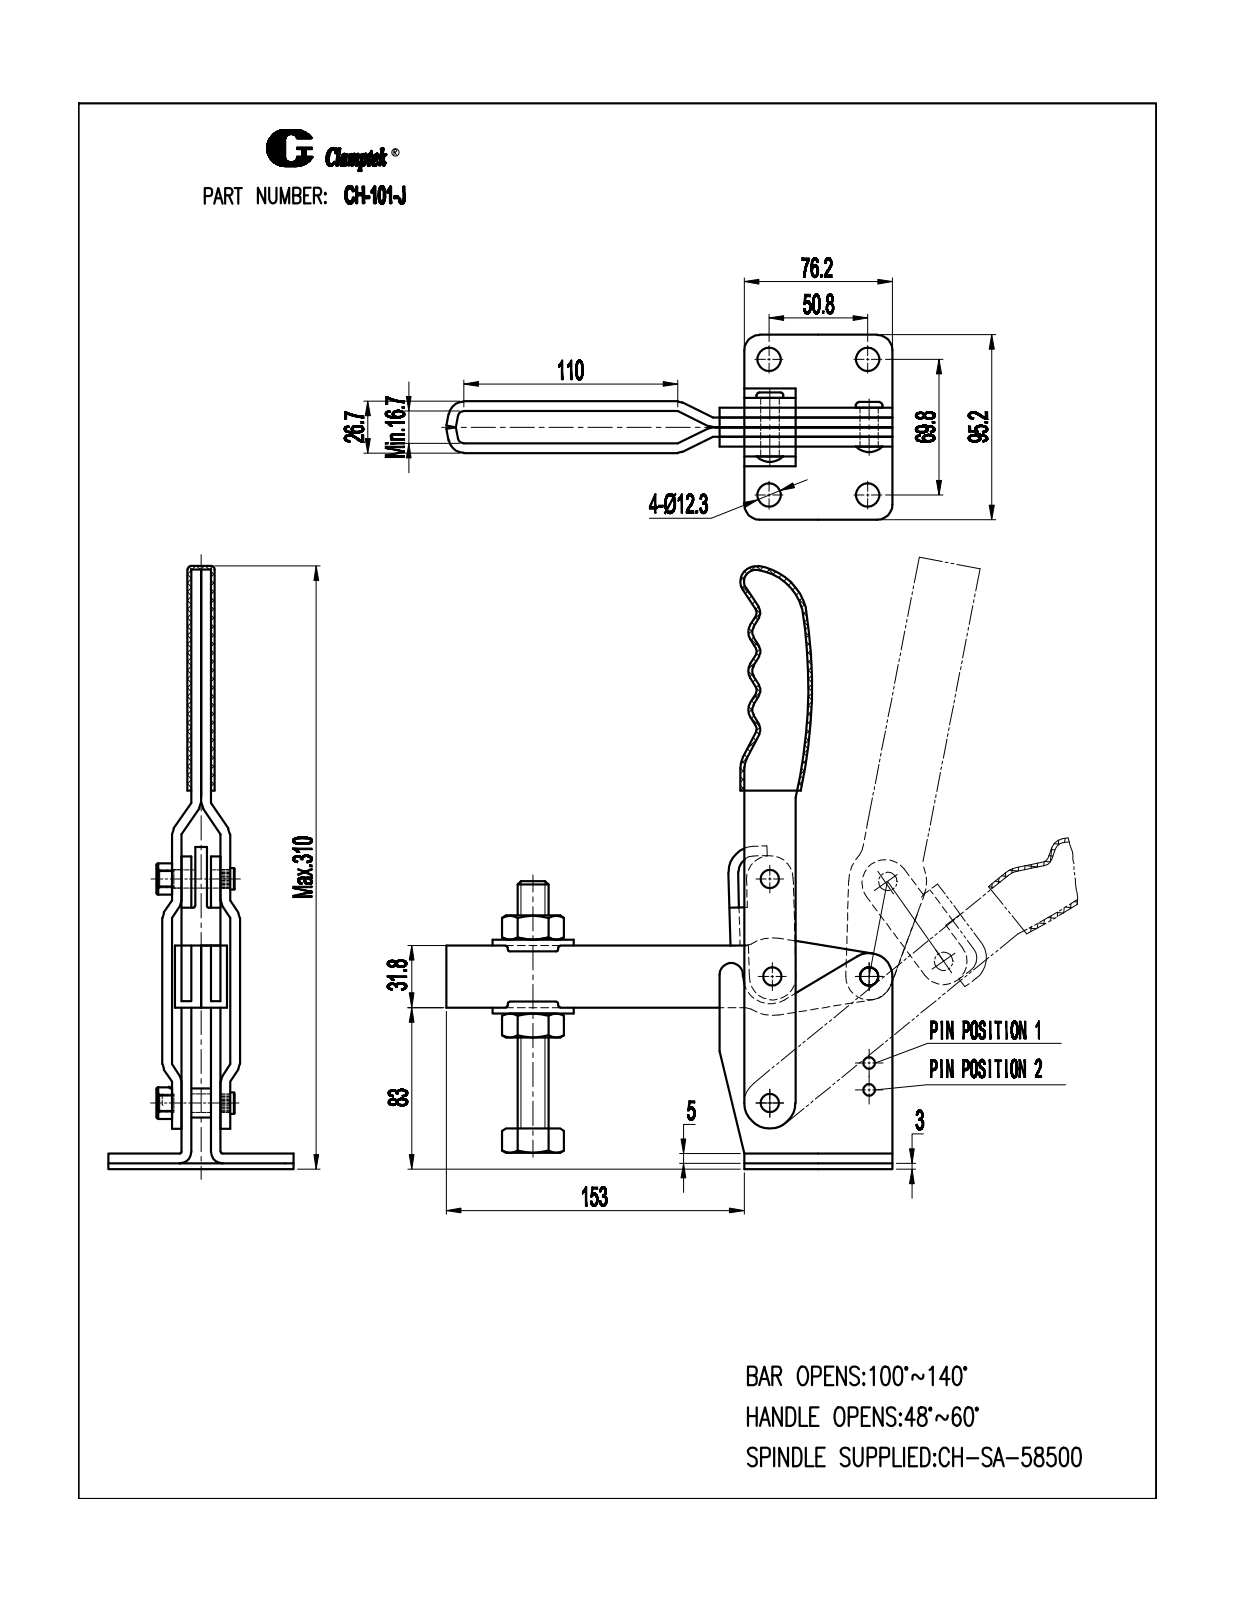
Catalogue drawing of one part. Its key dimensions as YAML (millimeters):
part_name: "CH-101-J-06; CH-101-J-03 HANDLE; 3-8-16 LOCK NUT; CH-10247-08 (+8 more)"
step_written_by: "SolidWorks 2010 (CONFIG_CONTROL_DESIGN)"
units: millimeters
bodies: {solids: 23, faces: 1069, planar: 364, cylindrical: 416, other: 289}
overall_size: [305.8, 228.35, 95.2]
volume: 347977
surface_area: 174510
round_holes:
  - {diameter: 12.3, count: 5}
  - {diameter: 12.5, count: 4}
  - {diameter: 12.7, count: 3}
  - {diameter: 6, count: 2}
  - {diameter: 8.5, count: 2}
  - {diameter: 9.5, count: 2}
  - {diameter: 16, count: 2}
  - {diameter: 4.02, count: 1}
  - {diameter: 5, count: 1}
  - {diameter: 13.7, count: 1}
round_bosses_or_shafts:
  - {diameter: 12, count: 4}
  - {diameter: 11, count: 2}
  - {diameter: 9.5, count: 2}
  - {diameter: 15, count: 1}
  - {diameter: 13.7, count: 1}
  - {diameter: 12.8, count: 1}
  - {diameter: 3.35, count: 1}
partial_cylinders:
  - {radius: 5, count: 26}
  - {radius: 1, count: 19}
  - {radius: 3, count: 6}
  - {radius: 3.5, count: 6}
  - {radius: 8, count: 5}
  - {radius: 5, count: 4}
  - {radius: 6.5, count: 3}
  - {radius: 12, count: 3}
face_to_face_distances: [5, 10, 15, 20, 1.65, 3.35, 8.35, 13.35, 18.35, 23.35]
hole_center_spacings: [50.8, 69.8, 86.33, 13.9, 44.4, 49.8, 50.19, 51.44]
